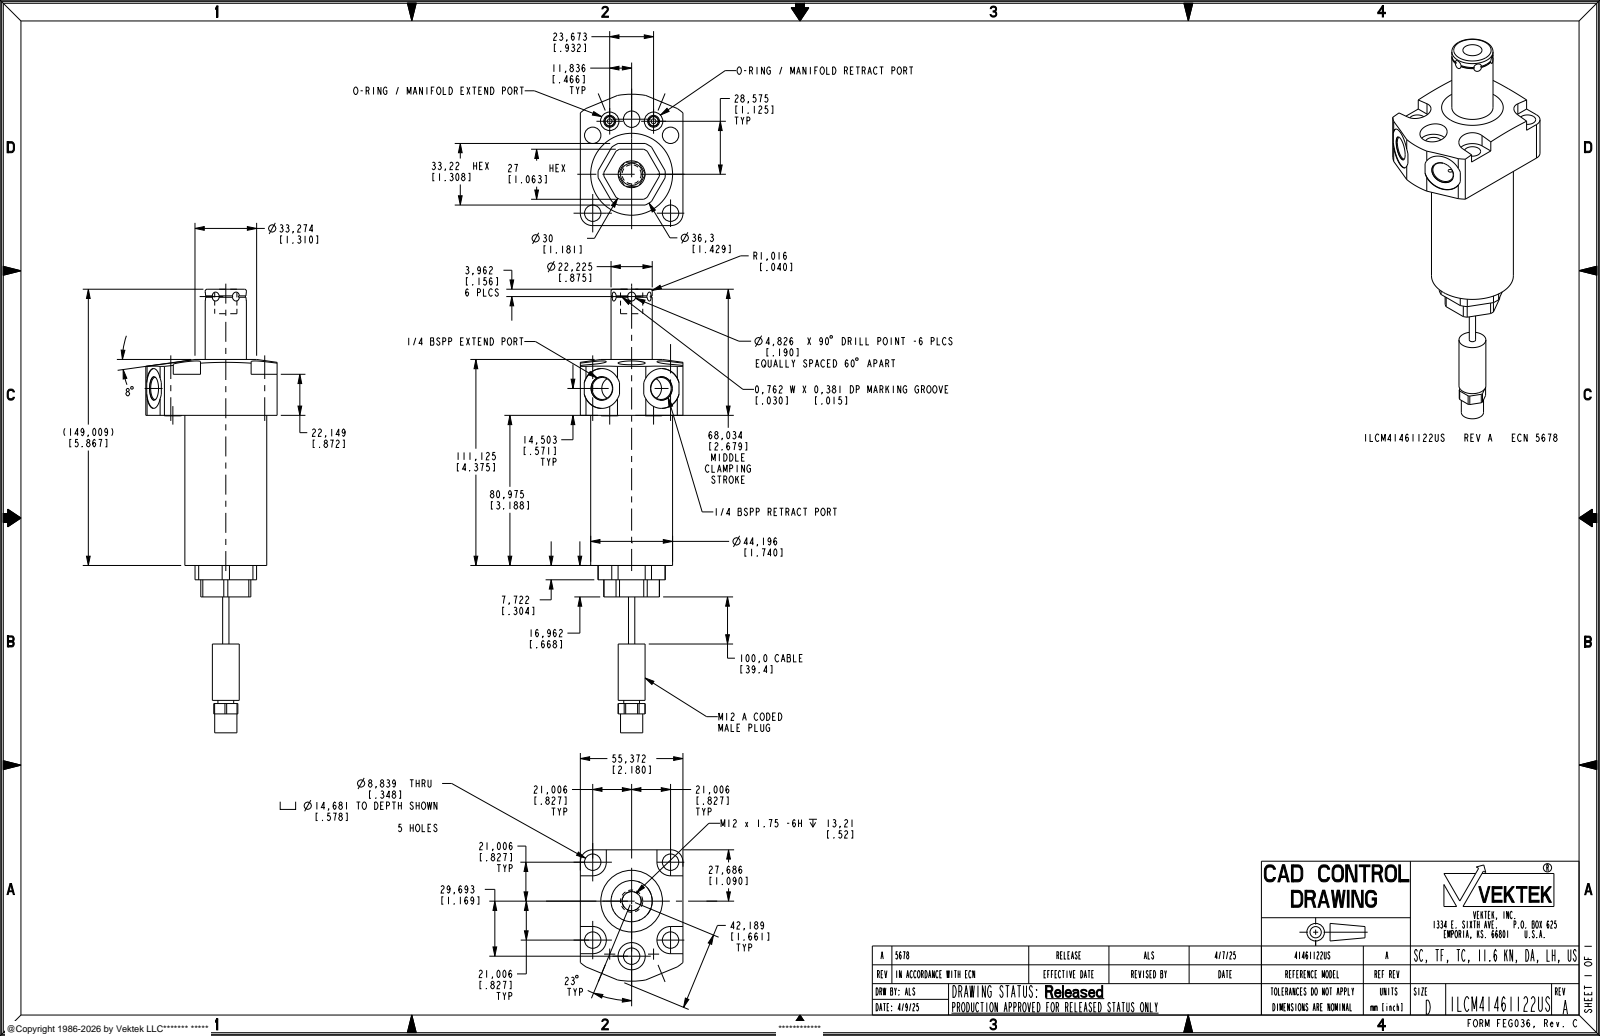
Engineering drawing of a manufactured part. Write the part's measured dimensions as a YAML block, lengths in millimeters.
part_name: "ILCM41461122US"
step_written_by: "CREO PARAMETRIC BY PTC INC, 2021164 (AUTOMOTIVE_DESIGN)"
units: millimeters
bodies: {solids: 1, faces: 211, planar: 90, cylindrical: 87, other: 34}
overall_size: [239.28, 77.22, 60.45]
volume: 249203
surface_area: 38183
round_holes:
  - {diameter: 8.84, count: 5}
  - {diameter: 2.49, count: 2}
  - {diameter: 6.5, count: 2}
  - {diameter: 9.96, count: 2}
  - {diameter: 11.89, count: 2}
  - {diameter: 21.5, count: 2}
  - {diameter: 10.31, count: 1}
  - {diameter: 14.68, count: 1}
round_bosses_or_shafts:
  - {diameter: 5.49, count: 2}
  - {diameter: 44.2, count: 1}
  - {diameter: 22.23, count: 1}
  - {diameter: 14.5, count: 1}
  - {diameter: 11.99, count: 1}
  - {diameter: 11.99, count: 1}
  - {diameter: 8.51, count: 1}
  - {diameter: 3.4, count: 1}
partial_cylinders:
  - {radius: 7.34, count: 4}
  - {radius: 6.48, count: 2}
  - {radius: 10.73, count: 1}
  - {radius: 15, count: 1}
  - {radius: 18.15, count: 1}
  - {radius: 43.18, count: 1}
face_to_face_distances: [55.38, 3.11, 30.11, 97.94, 16.97, 80.97, 120.09, 103.12, 22.15, 128.09]
hole_center_spacings: [29.71, 42.02, 11.88, 11.89, 22.73, 30.93, 33.71, 50.42]
